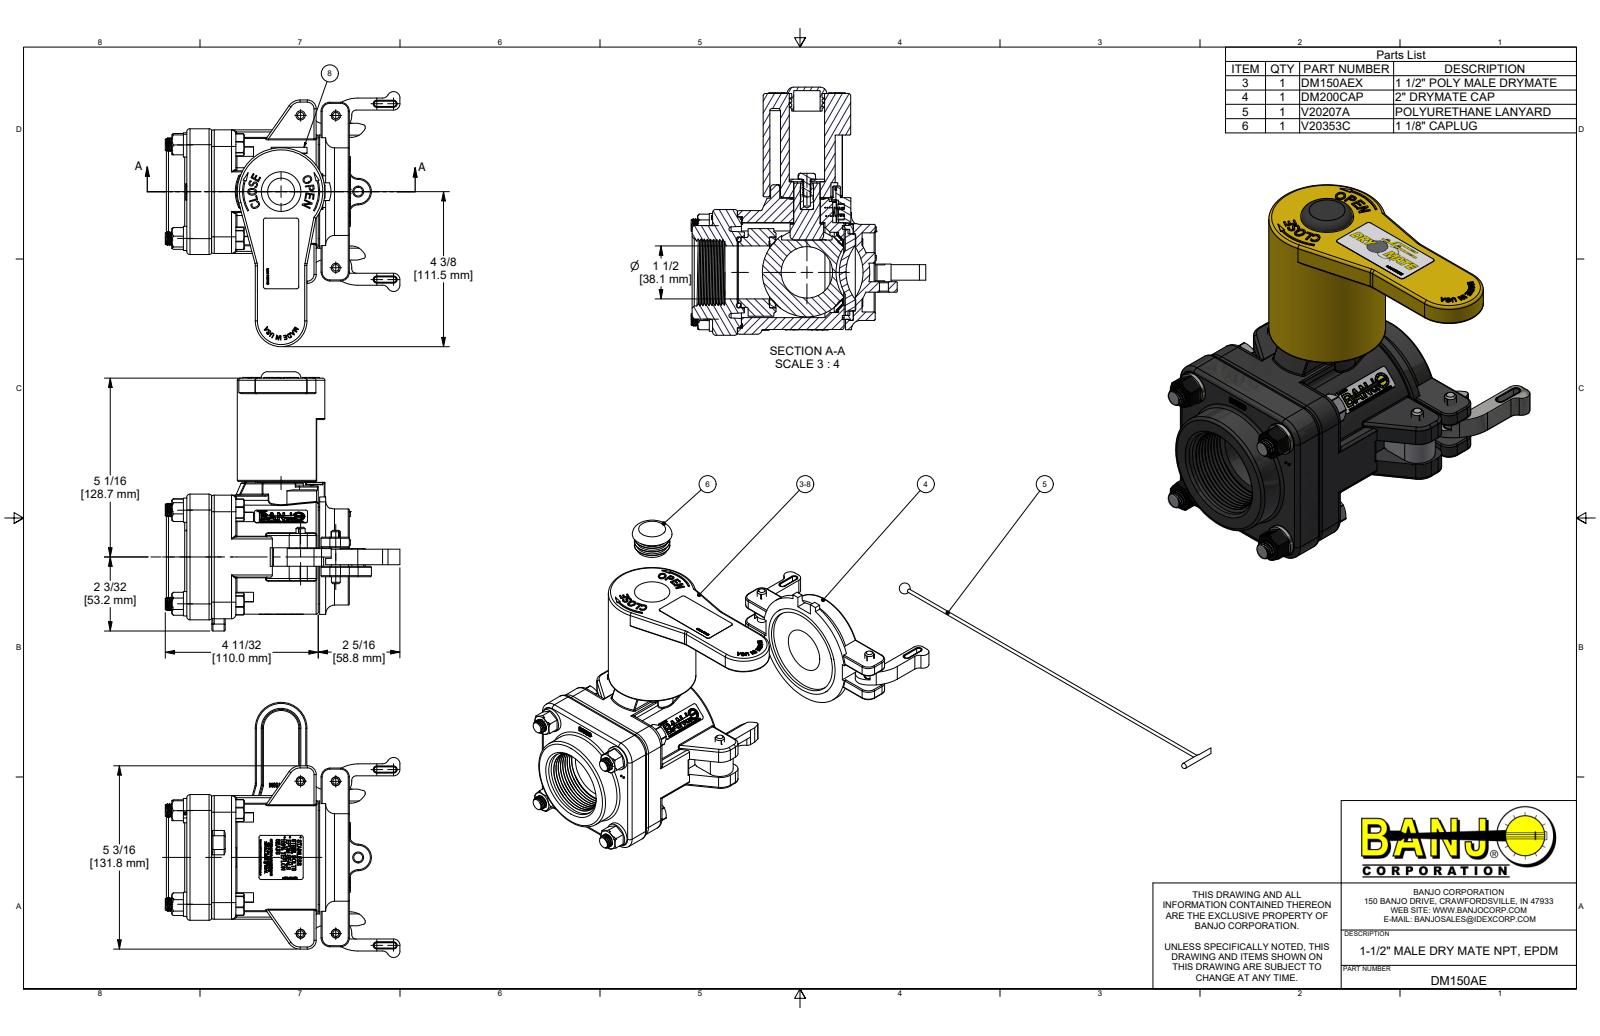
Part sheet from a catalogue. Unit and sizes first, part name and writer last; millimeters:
Units: millimetres
Overall size (bounding box): 186.4 × 183.4 × 168.8
Round holes (diameter × count): ⌀6.4 ×5, ⌀9.5 ×5, ⌀6.5 ×4, ⌀7.8 ×4, ⌀9.8 ×4, ⌀10.3 ×4, ⌀10.7 ×4, ⌀3.2 ×3, ⌀5 ×1, ⌀5.1 ×1, ⌀5.8 ×1, ⌀7.1 ×1
Round bosses / shafts (diameter × count): ⌀8.2 ×60, ⌀17.4 ×4, ⌀9.5 ×4, ⌀6.6 ×4, ⌀6.3 ×4, ⌀7.1 ×3, ⌀63 ×2, ⌀82.6 ×1
Partial cylindrical surfaces — rounded edges, fillets, slot ends (radius × count): R0.8 ×104, R1.5 ×52, R0.5 ×20, R0.3 ×12, R3.2 ×10, R6.4 ×10, R2.3 ×8, R4.1 ×8
Main face-to-face distances: 7.6, 89.7, 73.9, 94.6, 0.9, 7.5, 6.4, 0.8, 20.9, 83.3
Hole centre spacings: 67.4, 47.5, 47.8, 67.3, 67.5, 95.3, 24.1, 25.2
Volume: 829 200 mm³ · Surface area: 275 700 mm²
Bodies: 46 solids, 6037 faces (2879 planar, 890 cylindrical, 2268 other)
Part name (STEP PRODUCT): DM150AE; DM150AEX; DM20254; DM20254MY (+8 more)
STEP written by: Autodesk Inventor 2022 (AUTOMOTIVE_DESIGN)
